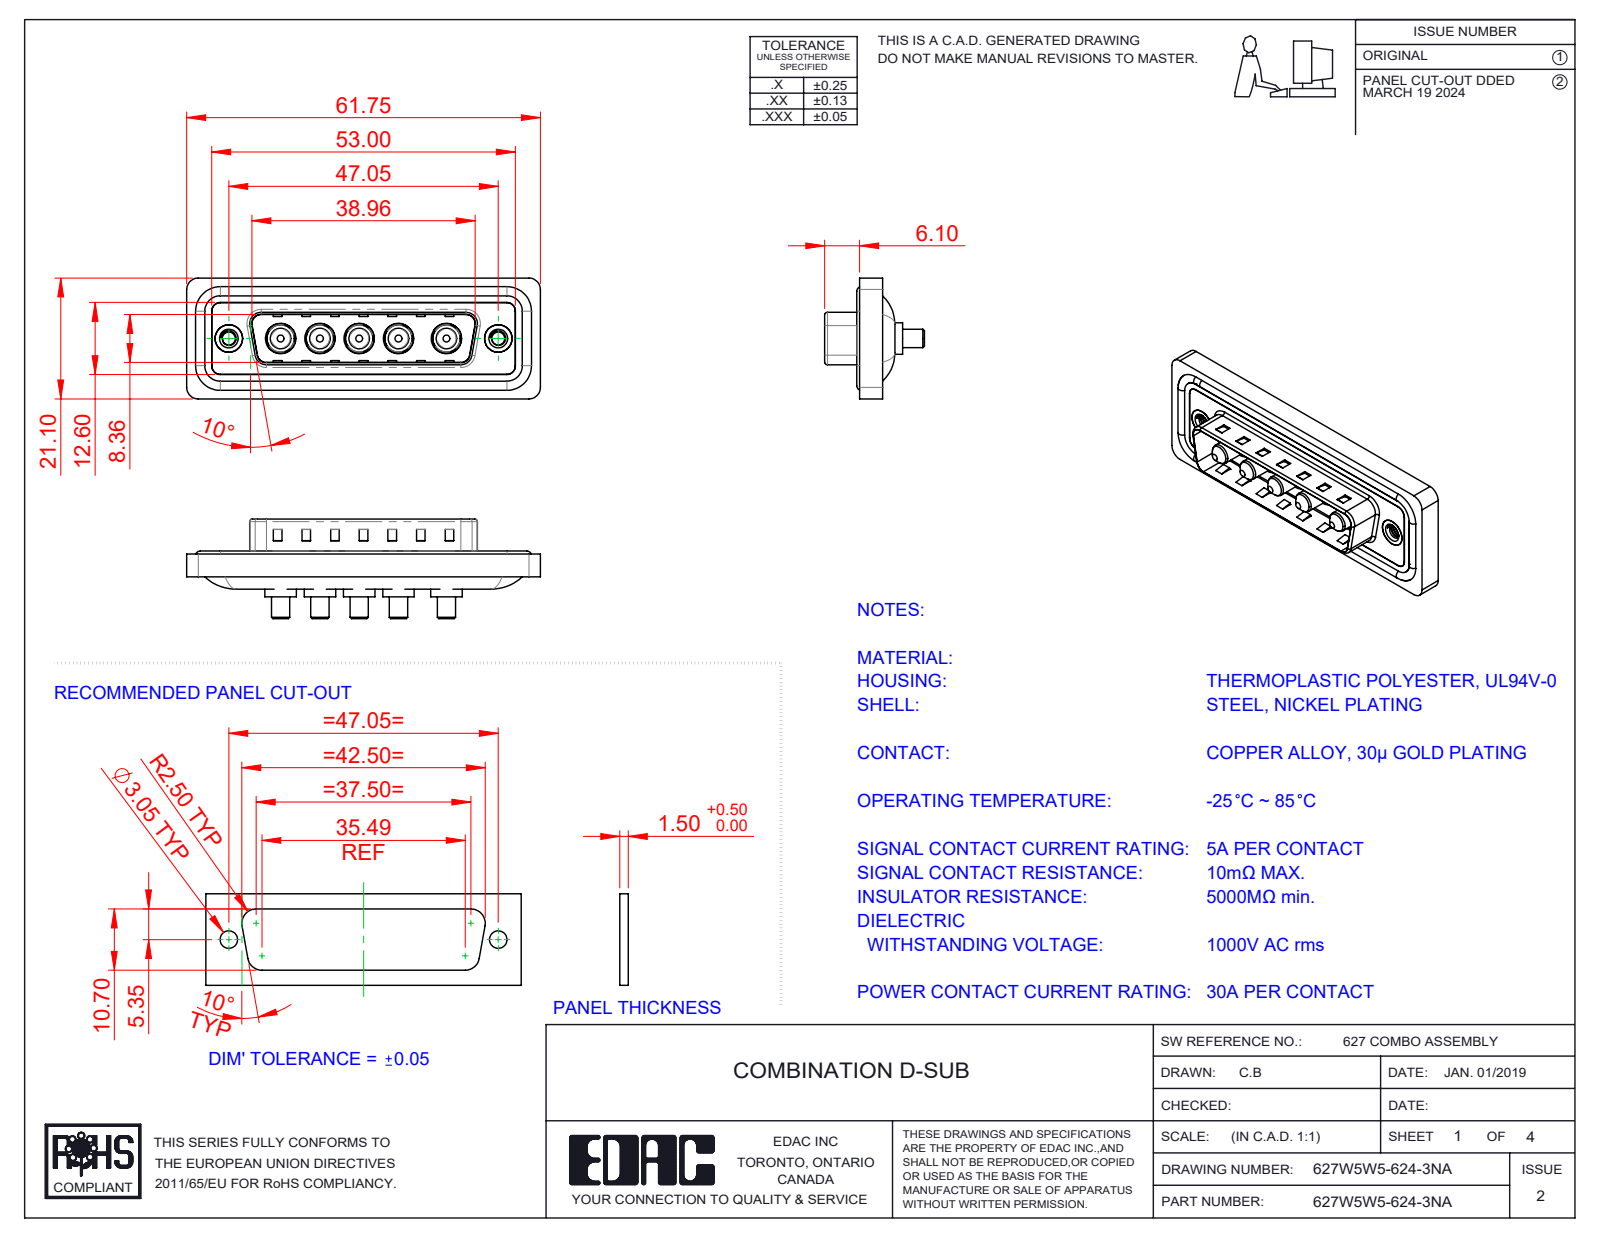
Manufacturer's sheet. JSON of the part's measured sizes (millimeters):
{"part_name": "627Combo Shell Rear_25 Contacts; Power Pin_30A S; 627Combo Housing_5W5; 627W5W5-624-3NA (+3 more)", "step_written_by": "SolidWorks 2023 (CONFIG_CONTROL_DESIGN)", "units": "millimeters", "bodies": {"solids": 17, "faces": 676, "planar": 259, "cylindrical": 285, "other": 132}, "overall_size": [61.75, 21.1, 17.4], "volume_mm3": 7510, "surface_area_mm2": 11817, "round_holes": [[4.85, 5], [5.3, 5], [2.26, 2], [4, 2], [4.8, 2], [5, 2]], "round_bosses_or_shafts": [[5.5, 5], [5.2, 5], [4.75, 5], [3.75, 5], [3.6, 5], [3.2, 5], [1.6, 4], [4.9, 2]], "partial_cylinders_radius": [[1.5, 22], [2, 18], [0.5, 8], [1.6, 8], [2.1, 5], [0.25, 4], [0.6, 4], [0.65, 4]], "face_to_face_distances": [0.4, 1.5, 0.5, 1.1, 3.1, 1.6, 2.9, 0.82, 9.58, 5.65], "hole_center_spacings": [6.86, 9.04, 13.73, 38.01, 6.87, 8.37, 8.38, 9.05]}
